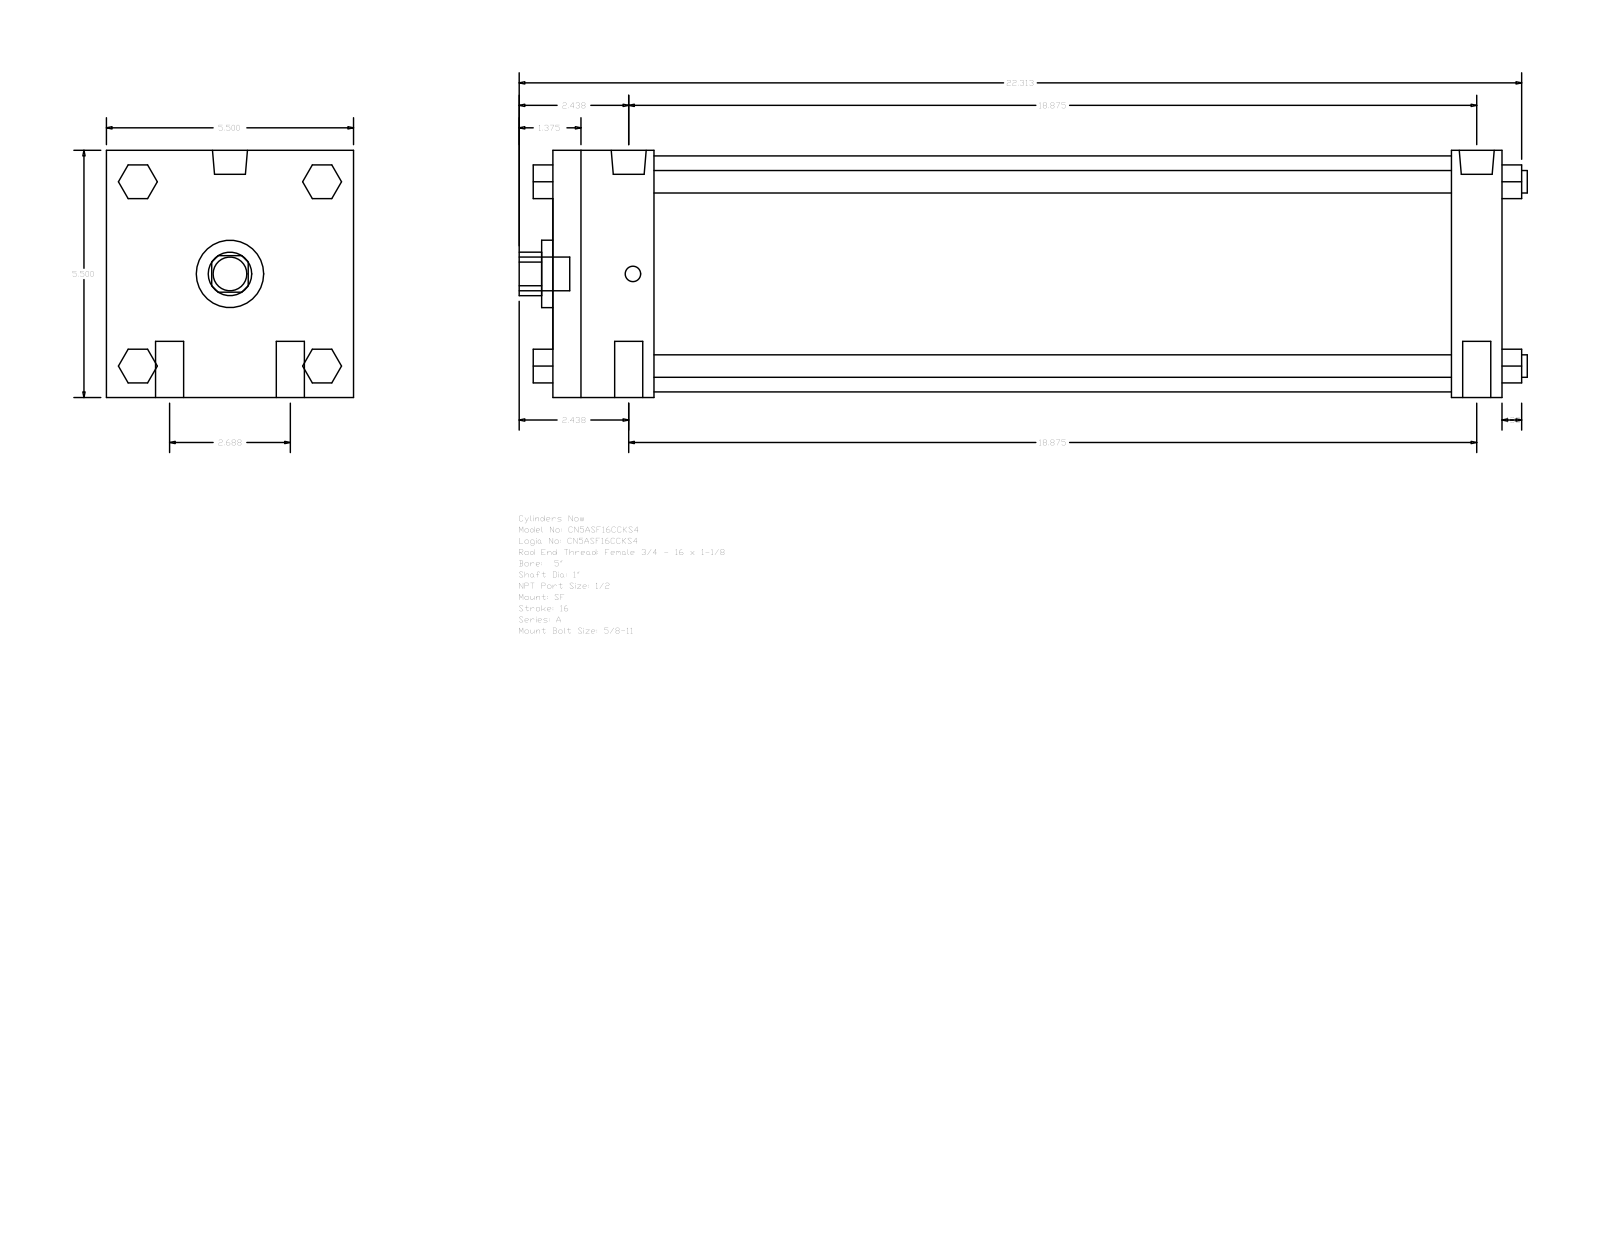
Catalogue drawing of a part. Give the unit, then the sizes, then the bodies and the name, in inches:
Units: inches
Overall size (bounding box): 22.437 × 5.5 × 5.5
Round holes (diameter × count): ⌀1 ×1, ⌀1.5 ×1, ⌀5.25 ×1
Round bosses / shafts (diameter × count): ⌀0.625 ×4, ⌀0.5 ×4, ⌀0.778 ×2, ⌀0.344 ×2, ⌀0.75 ×1
Partial cylindrical surfaces — rounded edges, fillets, slot ends (radius × count): R0.484 ×1
Main face-to-face distances: 5.5, 21.125, 1.125, 2.25, 20, 17.75, 18.875, 0.75, 2.05, 3.55
Bodies: 0 solids, 124 faces (94 planar, 30 cylindrical, 0 other)
Part name (STEP PRODUCT): A_SF__0500_1
STEP written by: GSSL Pune (CONFIG_CONTROL_DESIGN)
